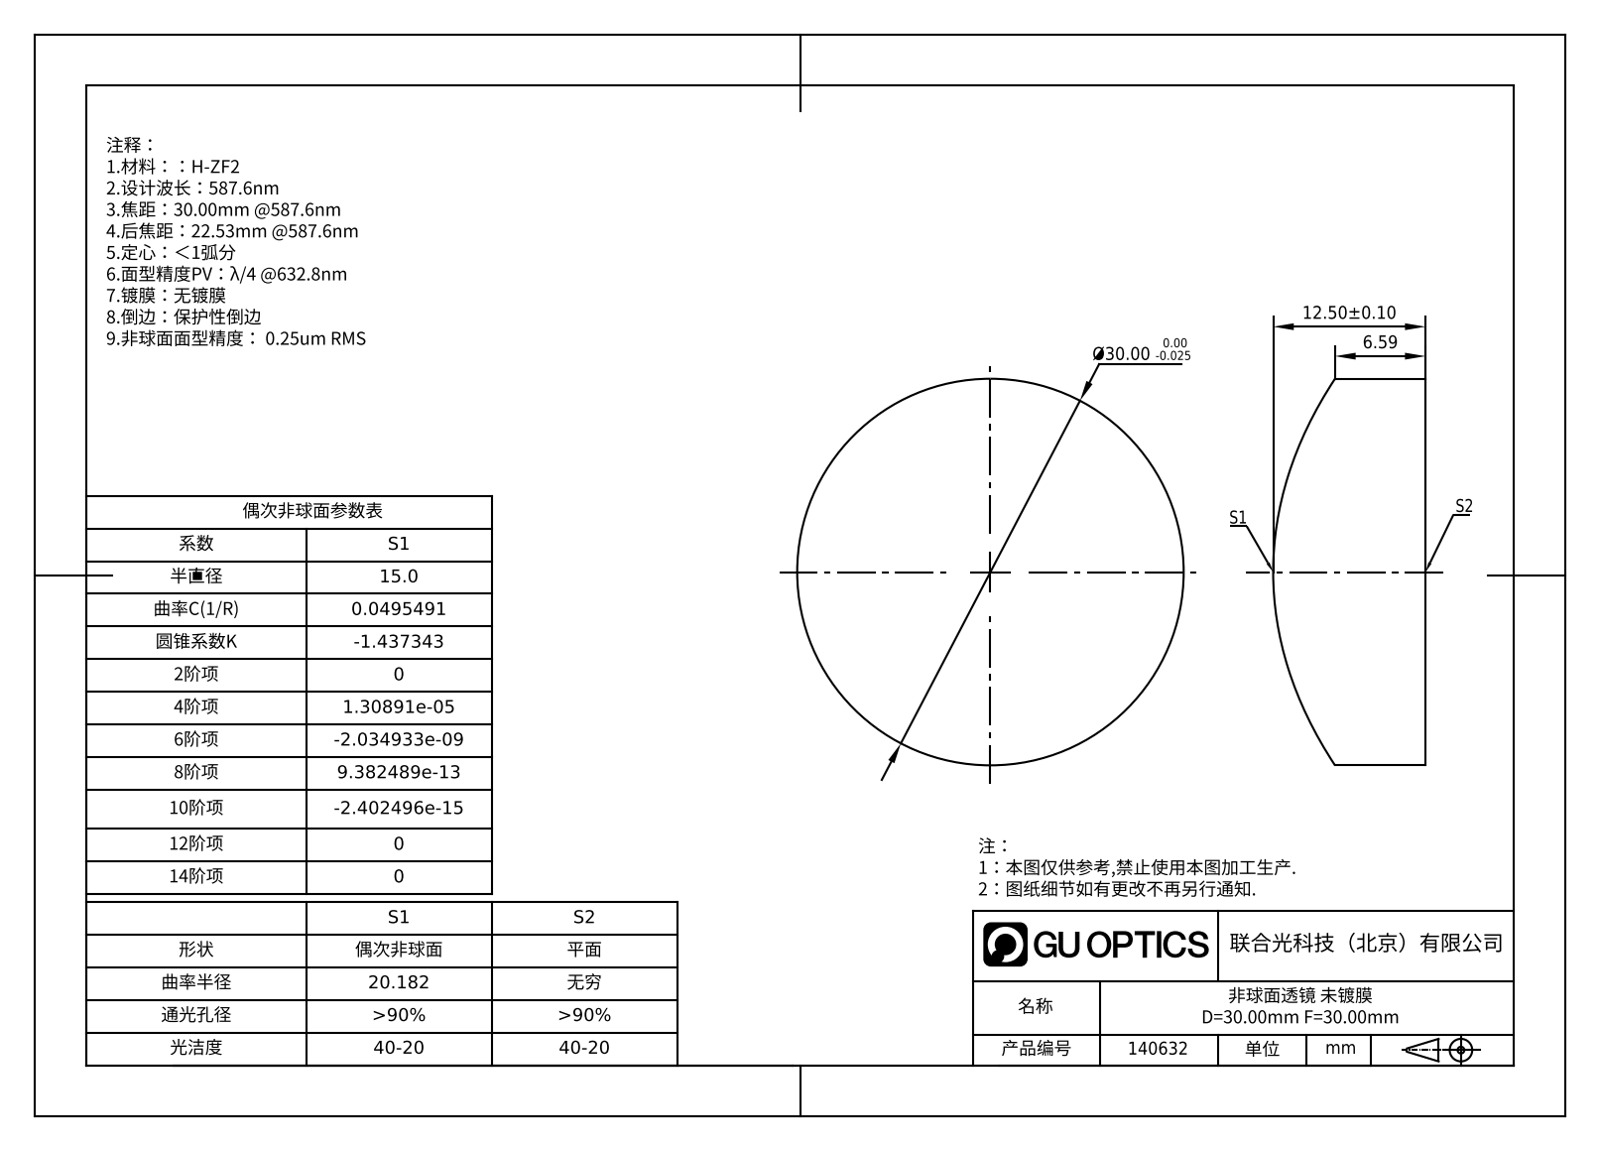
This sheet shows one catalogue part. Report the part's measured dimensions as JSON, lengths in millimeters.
{"part_name": "GLA11-030-030-H; GLA11-030-030-H.stp; surfaces 1,2.stp", "step_written_by": "SolidWorks 2023 (CONFIG_CONTROL_DESIGN)", "units": "millimeters", "bodies": {"solids": 1, "faces": 5, "planar": 1, "cylindrical": 2, "other": 2}, "overall_size": [30, 30, 12.5], "volume_mm3": 6786, "surface_area_mm2": 2138, "round_bosses_or_shafts": [[30, 1]]}
